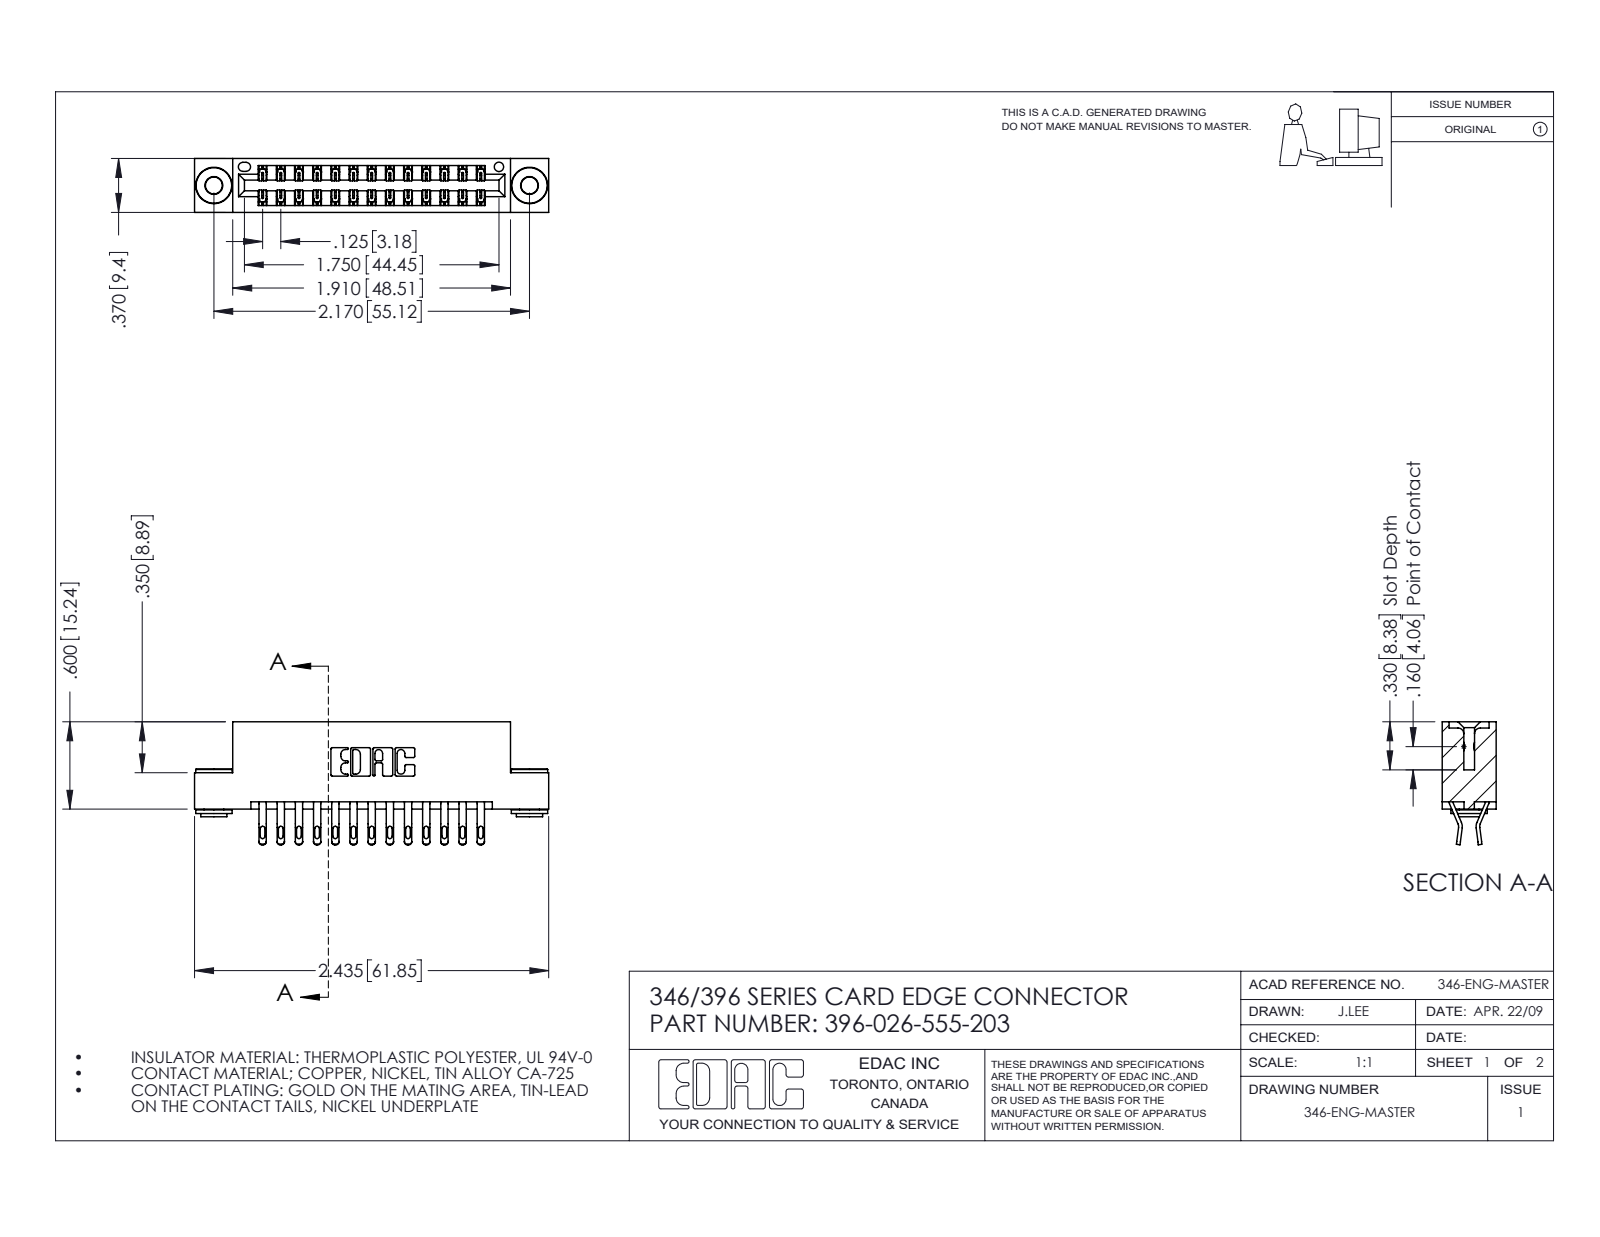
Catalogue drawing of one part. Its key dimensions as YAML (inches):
part_name: "345-292-001_555 Tail; 346 Part_Flush Mounting Lugs - 0.156 Dia-TH; 345-250-002_345-250-002-102; 396-026-555-203"
step_written_by: "SolidWorks 2016 (CONFIG_CONTROL_DESIGN)"
units: inches
bodies: {solids: 29, faces: 1668, planar: 944, cylindrical: 716, other: 8}
overall_size: [2.435, 0.845, 0.37]
volume: 0.36
surface_area: 12.61
round_holes:
  - {diameter: 0.116, count: 2}
  - {diameter: 0.156, count: 2}
  - {diameter: 0.064, count: 1}
round_bosses_or_shafts:
  - {diameter: 0.25, count: 2}
  - {diameter: 0.18, count: 2}
  - {diameter: 0.136, count: 2}
partial_cylinders:
  - {radius: 0.016, count: 52}
  - {radius: 0.02, count: 52}
  - {radius: 0.006, count: 39}
  - {radius: 0.01, count: 22}
  - {radius: 0.007, count: 6}
  - {radius: 0.031, count: 6}
  - {radius: 0.026, count: 3}
  - {radius: 0.01, count: 2}
face_to_face_distances: [0.25, 0.048, 0.322, 0.37, 0.025, 0.072, 0.298, 0.275, 0.148, 0.222]
hole_center_spacings: [0.246, 1.964, 2.17]
